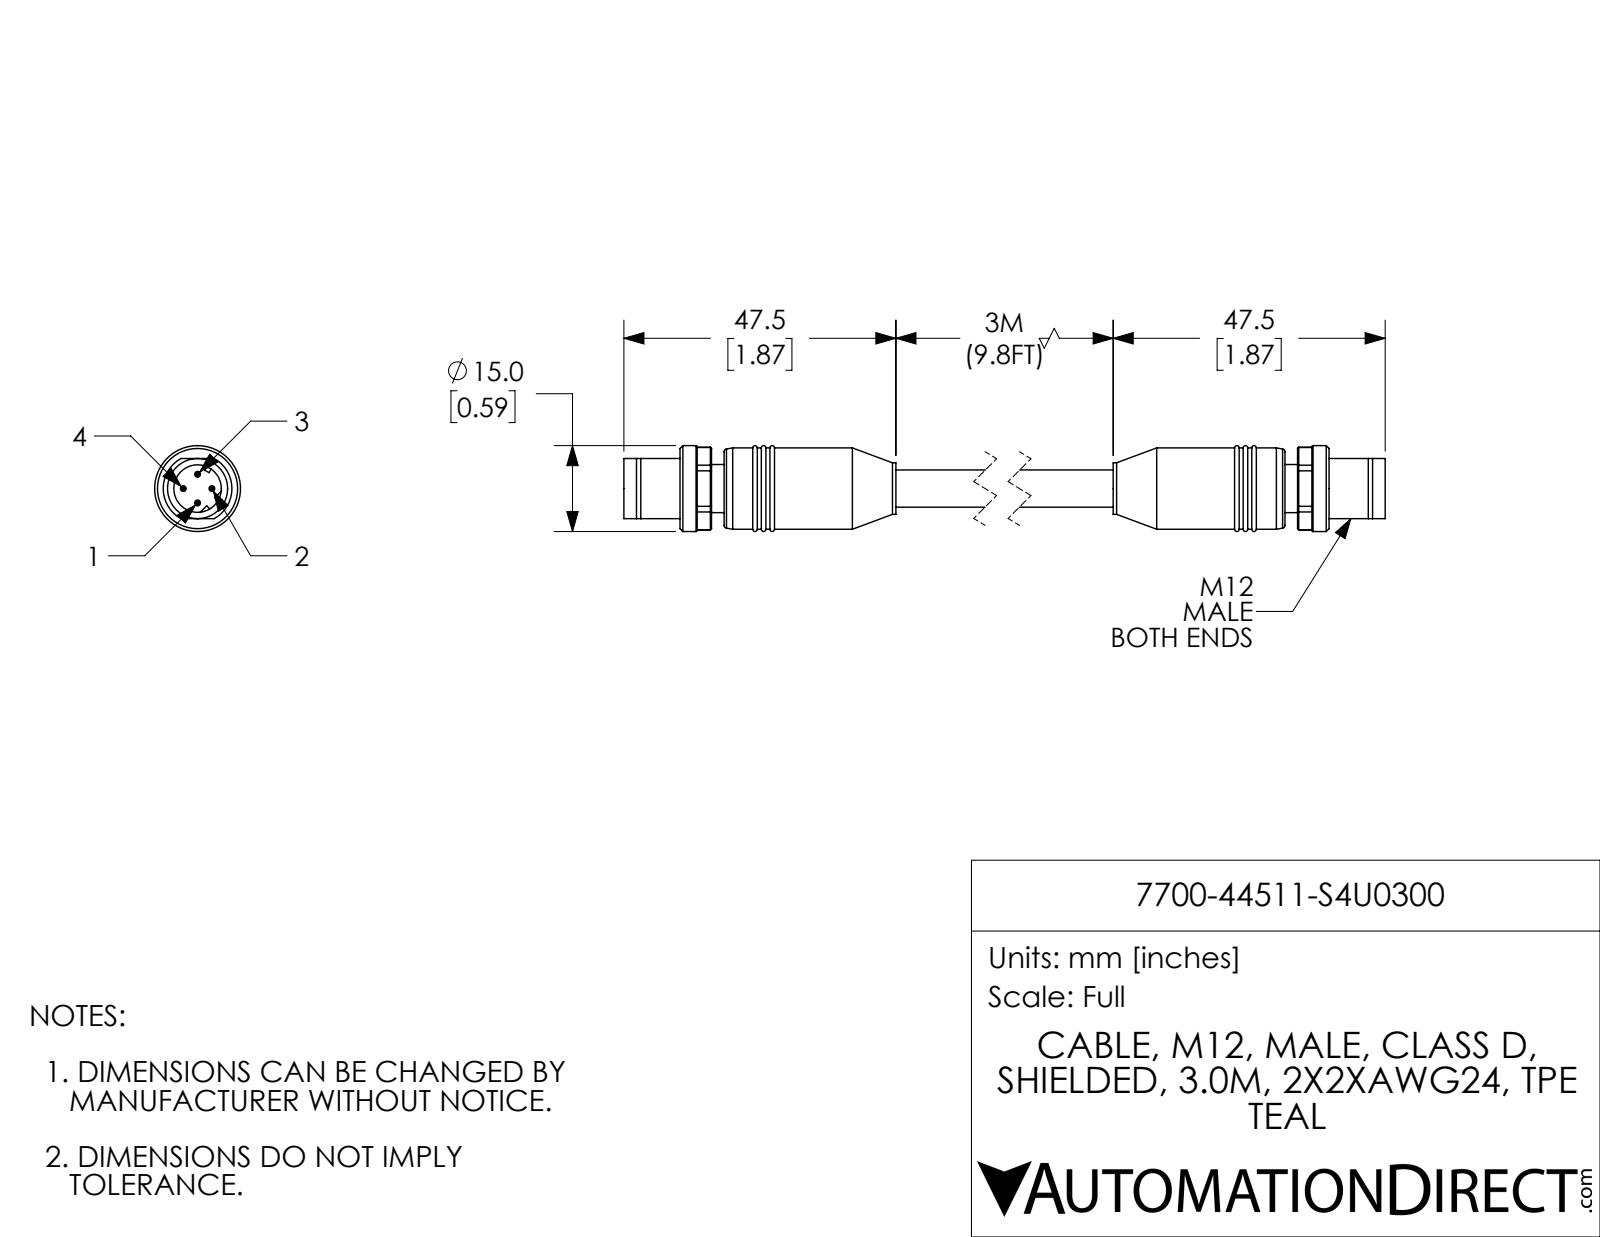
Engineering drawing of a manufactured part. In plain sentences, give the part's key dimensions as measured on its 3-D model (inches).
The part is named "7700-44511-S4U0300_MALE; 7700-44511-S4U0300". Its 3-D file was written by "SolidWorks 2017 (AUTOMOTIVE_DESIGN)". It is 2 solids with 226 faces: 72 planar, 74 cylindrical and 80 other. Overall it measures 5.787 by 0.591 by 0.591 inches. Its volume is 0.804 cubic inches and its surface area 9.846 square inches. Round holes: 1 of diameter 0.327. Round bosses or shafts: 4 of diameter 0.039, 1 of diameter 0.591, 1 of diameter 0.559, 1 of diameter 0.413, 1 of diameter 0.354, 1 of diameter 0.331, 1 of diameter 0.256. Partial cylindrical surfaces (rounded edges, fillets, slot ends): 1 of radius 0.236, 1 of radius 0.283. The main face-to-face distances are 0.087, 4.496, 0.035, 0.252, 0.339, 4.748, 4.835, 5.051, 0.217, 0.303.
